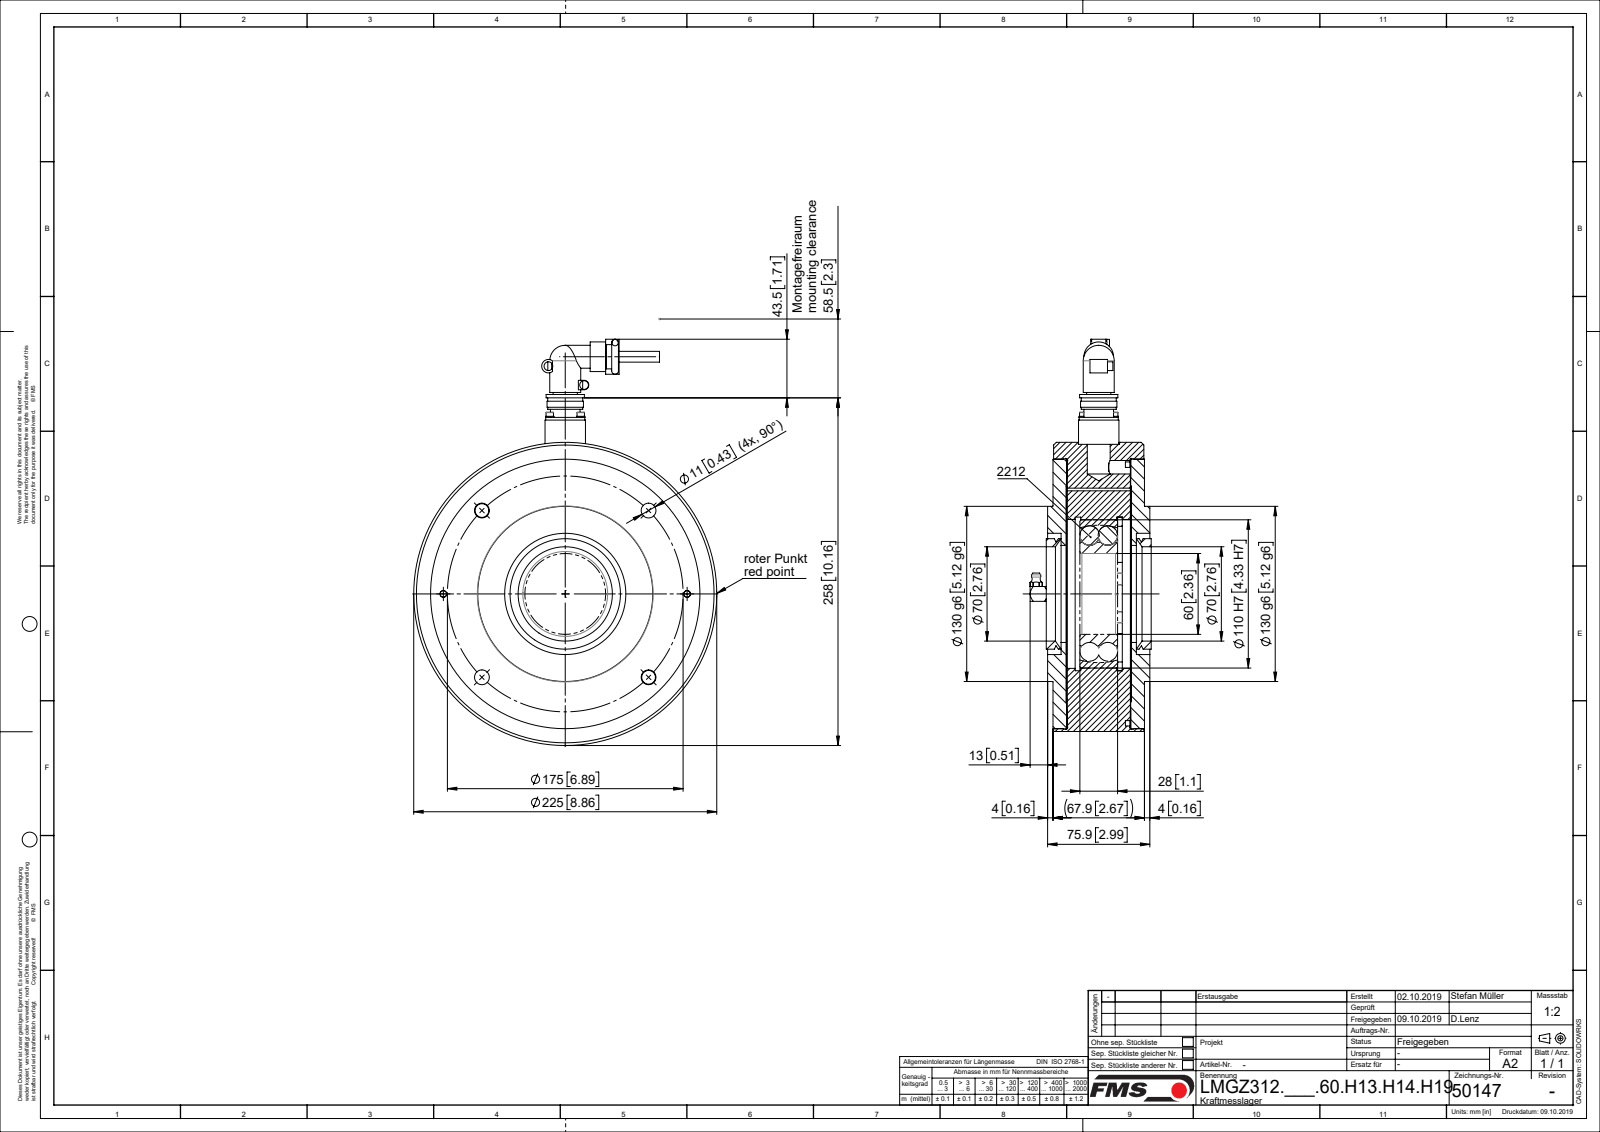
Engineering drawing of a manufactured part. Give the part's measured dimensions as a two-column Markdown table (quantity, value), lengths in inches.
| quantity | value |
| --- | --- |
| part name | L50147; L4785904; TEIL1; L49026 (+8 more) |
| STEP written by | Mechanical Desktop 2007 (CONFIG_CONTROL_DESIGN) |
| units | inches |
| bodies | 22 solids, 448 faces (133 planar, 244 cylindrical, 71 other) |
| overall size | 11.87 × 8.858 × 3.559 |
| volume | 145.7 in³ |
| surface area | 616 in² |
| round holes (diameter × count) | 0.433 × 6, 0.102 × 4, 0.126 × 4, 0.134 × 4, 0.138 × 4, 0.354 × 4, 0.197 × 2, 0.236 × 2, 0.26 × 2, 0.342 × 1, 0.906 × 1, 2.362 × 1 |
| round bosses / shafts (diameter × count) | 0.244 × 4, 0.217 × 4, 0.118 × 4, 0.394 × 3, 0.866 × 2, 0.315 × 2, 0.256 × 2, 0.189 × 2 |
| partial cylindrical surfaces (radius × count) | 0.098 × 2, 0.138 × 1, 0.197 × 1, 3.189 × 1, 3.386 × 1 |
| main face-to-face distances | 1.86, 0.411, 0.402, 2.262, 2.272, 1.87, 0.02, 1.89, 0.382, 2.291 |
| hole center spacings | 0.64, 0.906, 2.684, 3.445, 4.872, 6.474, 1.281, 2.451 |
